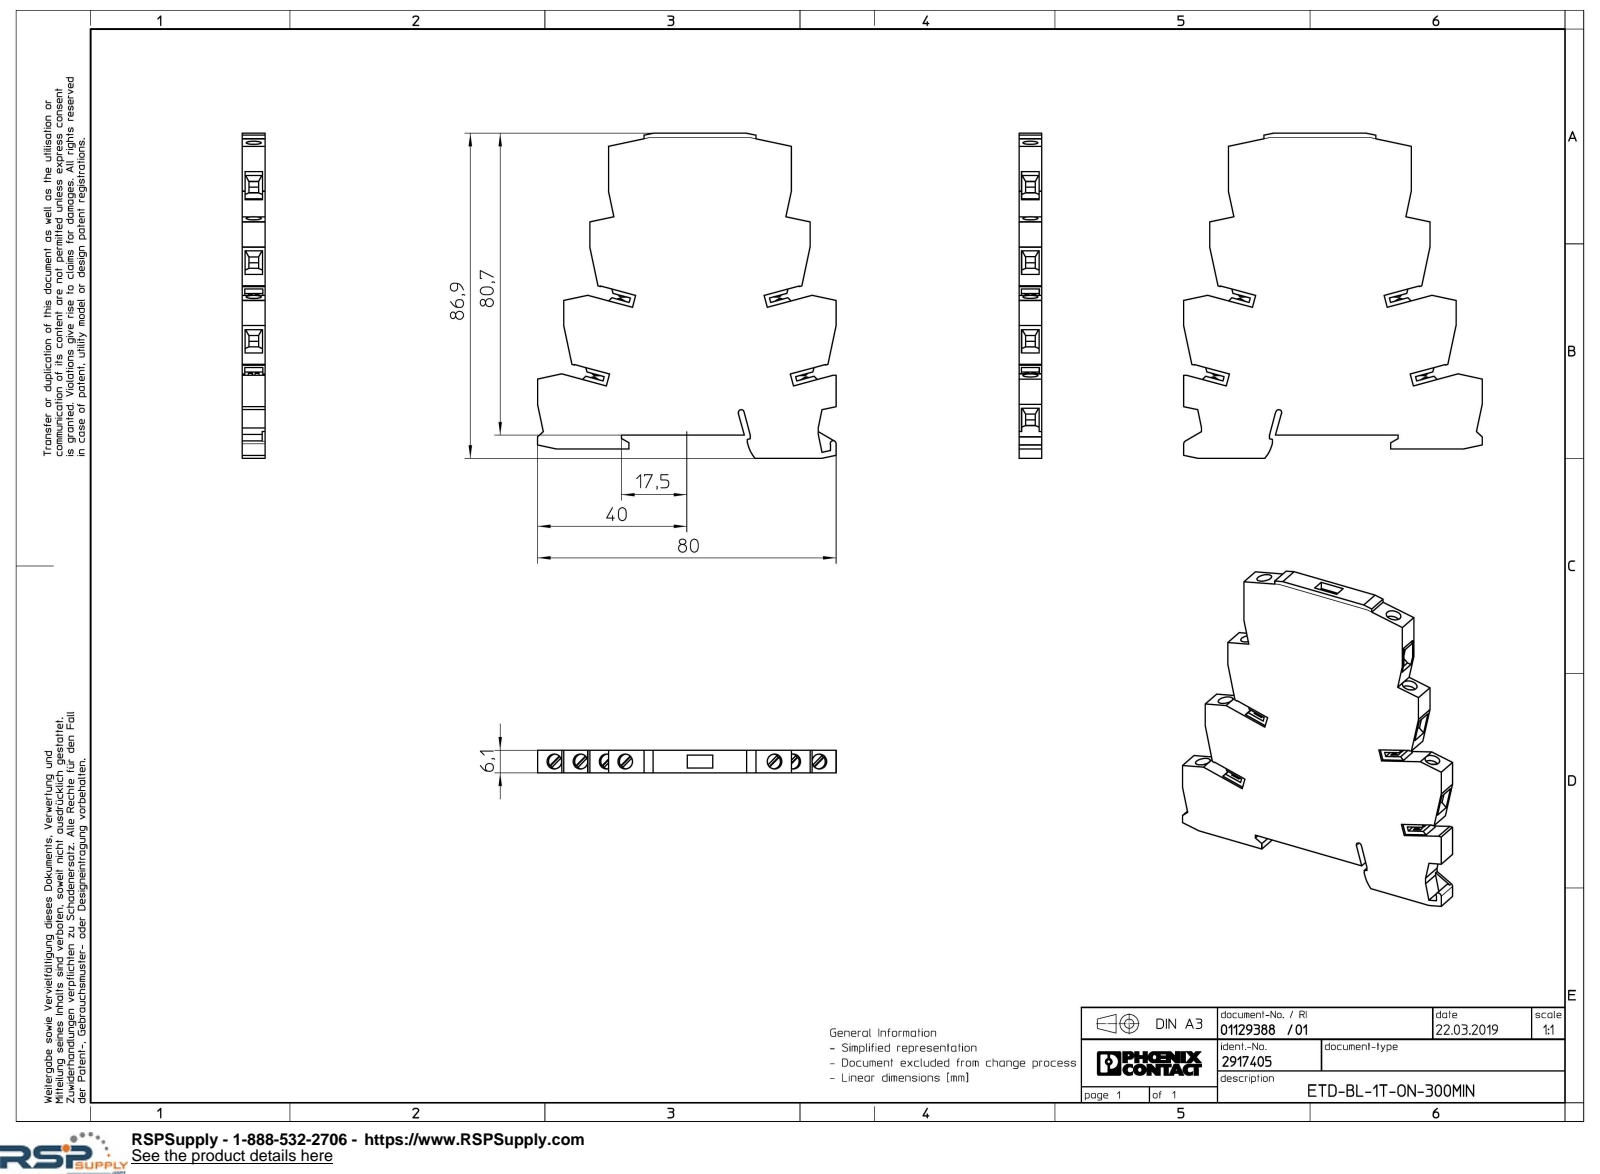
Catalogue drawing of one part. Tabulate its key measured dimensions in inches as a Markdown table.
| quantity | value |
| --- | --- |
| part name | ETD-BL-1T-...-SC-select |
| STEP written by | Creo Elements/Direct Modeling 20.1A 29-Sep-2018 (C) Parametric Technology GmbH (AUTOMOTIVE_DESIGN) |
| units | inches |
| bodies | 1 solid, 332 faces (315 planar, 17 cylindrical, 0 other) |
| overall size | 3.421 × 3.15 × 0.24 |
| volume | 1.836 in³ |
| surface area | 21.82 in² |
| round holes (diameter × count) | 0.157 × 7 |
| partial cylindrical surfaces (radius × count) | 0.031 × 2, 0.374 × 1 |
| main face-to-face distances | 0.24, 0.069, 0.171, 0.041, 0.146, 0.87, 0.028, 0.102, 0.213, 0.144 |
| hole center spacings | 0.442, 0.358, 0.358, 0.8, 0.8, 0.883, 1.241 |
